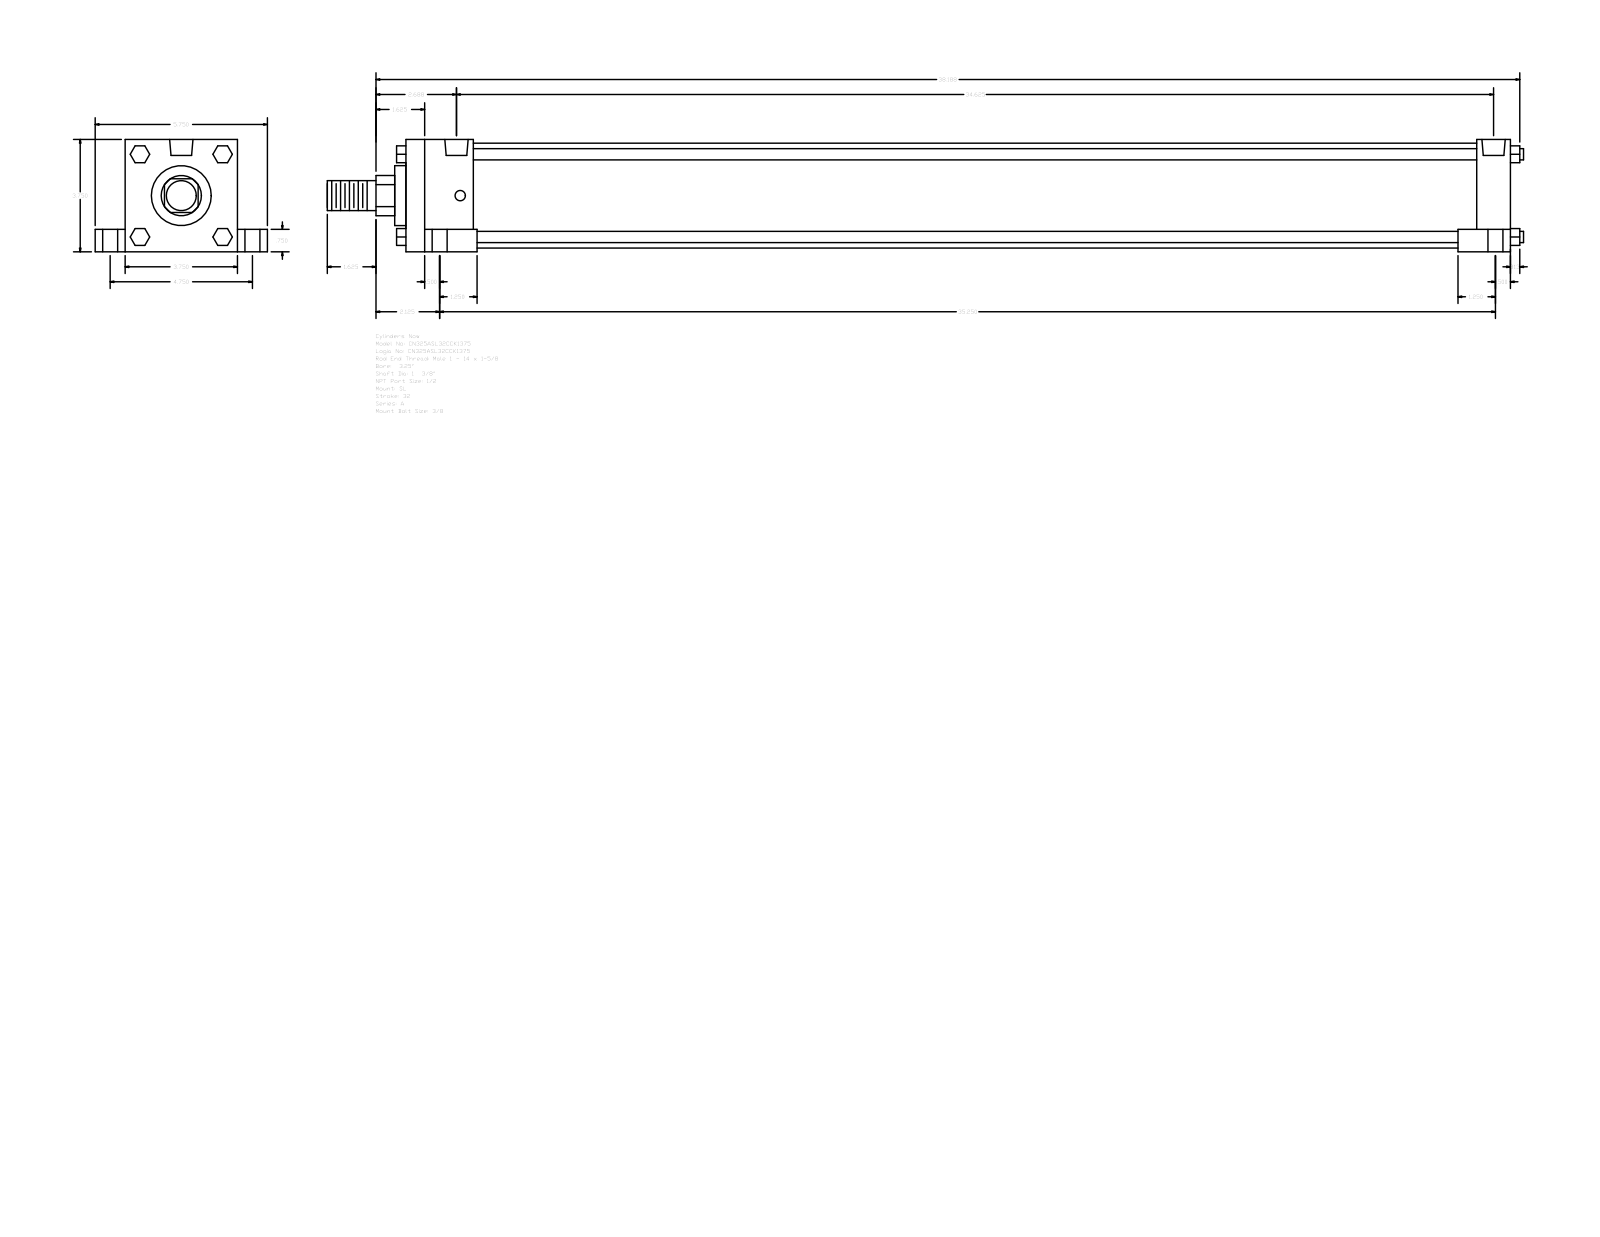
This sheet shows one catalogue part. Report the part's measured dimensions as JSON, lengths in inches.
{"part_name": "A_SL__0325_1.375", "step_written_by": "GSSL Pune (CONFIG_CONTROL_DESIGN)", "units": "inches", "bodies": {"solids": 0, "faces": 150, "planar": 114, "cylindrical": 36, "other": 0}, "overall_size": [39.937, 5.75, 3.75], "round_holes": [[0.344, 4], [0.5, 4], [0.75, 4], [0.778, 2]], "round_bosses_or_shafts": [[0.375, 4], [3.5, 1], [2, 1], [1.375, 1], [1, 1]], "partial_cylinders_radius": [[0.672, 1]], "face_to_face_distances": [3.75, 36.875, 1, 4.75, 0.75, 3, 2.25, 1.125, 35.75, 33.5], "hole_center_spacings": [0.125, 2.376, 2.383, 2.441, 2.473, 4.75, 34.375, 34.5]}
